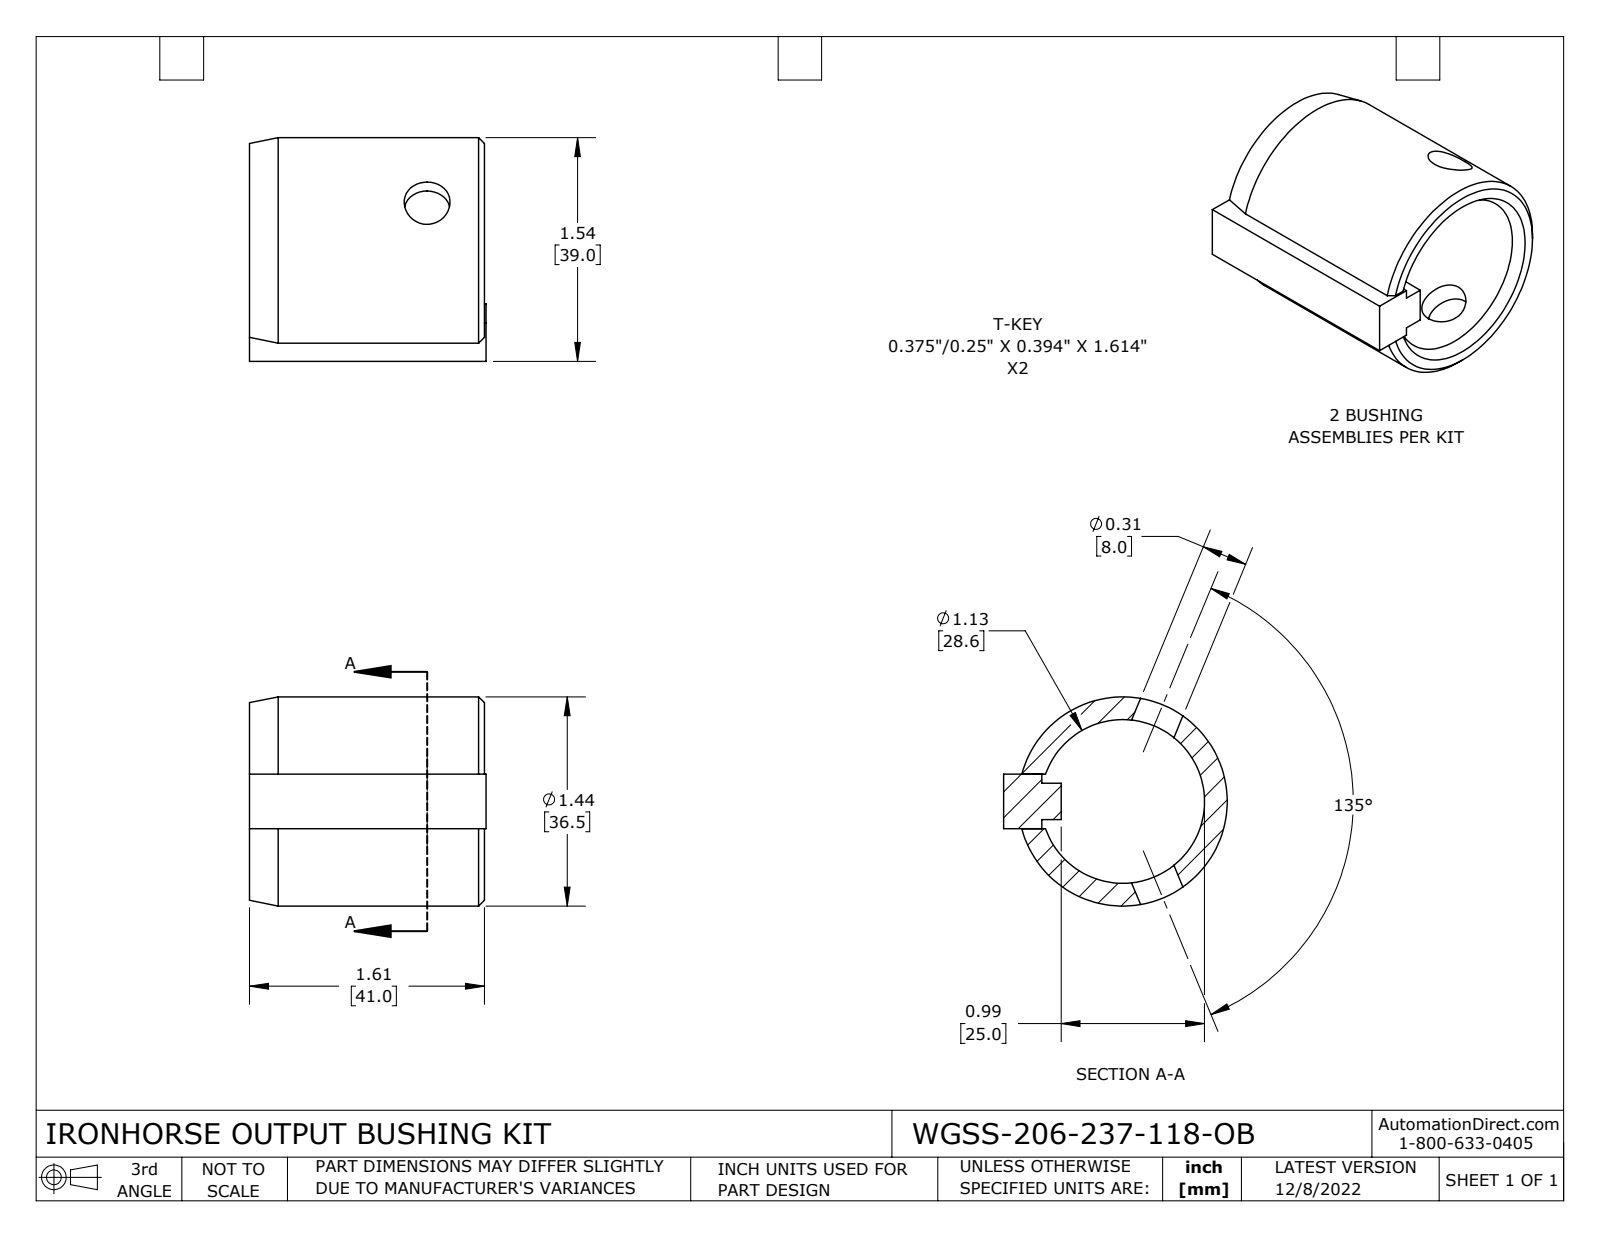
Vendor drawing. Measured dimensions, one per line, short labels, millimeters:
name: WGSS-206-237-118-OB
written by: SolidWorks 2021 (CONFIG_CONTROL_DESIGN)
unit: mm
bodies: 2 solids, 38 faces (16 planar, 10 cylindrical, 12 other)
size: 41.28 × 39.05 × 36.51
volume: 17 667 mm³; area: 10 143 mm²
holes: 2× ⌀8, 1× ⌀28.57
bosses: 1× ⌀36.51
face distances: 9.53, 1.59, 7.94, 10.04, 41, 6.35, 3.38, 6.66, 41.28, 1.58
